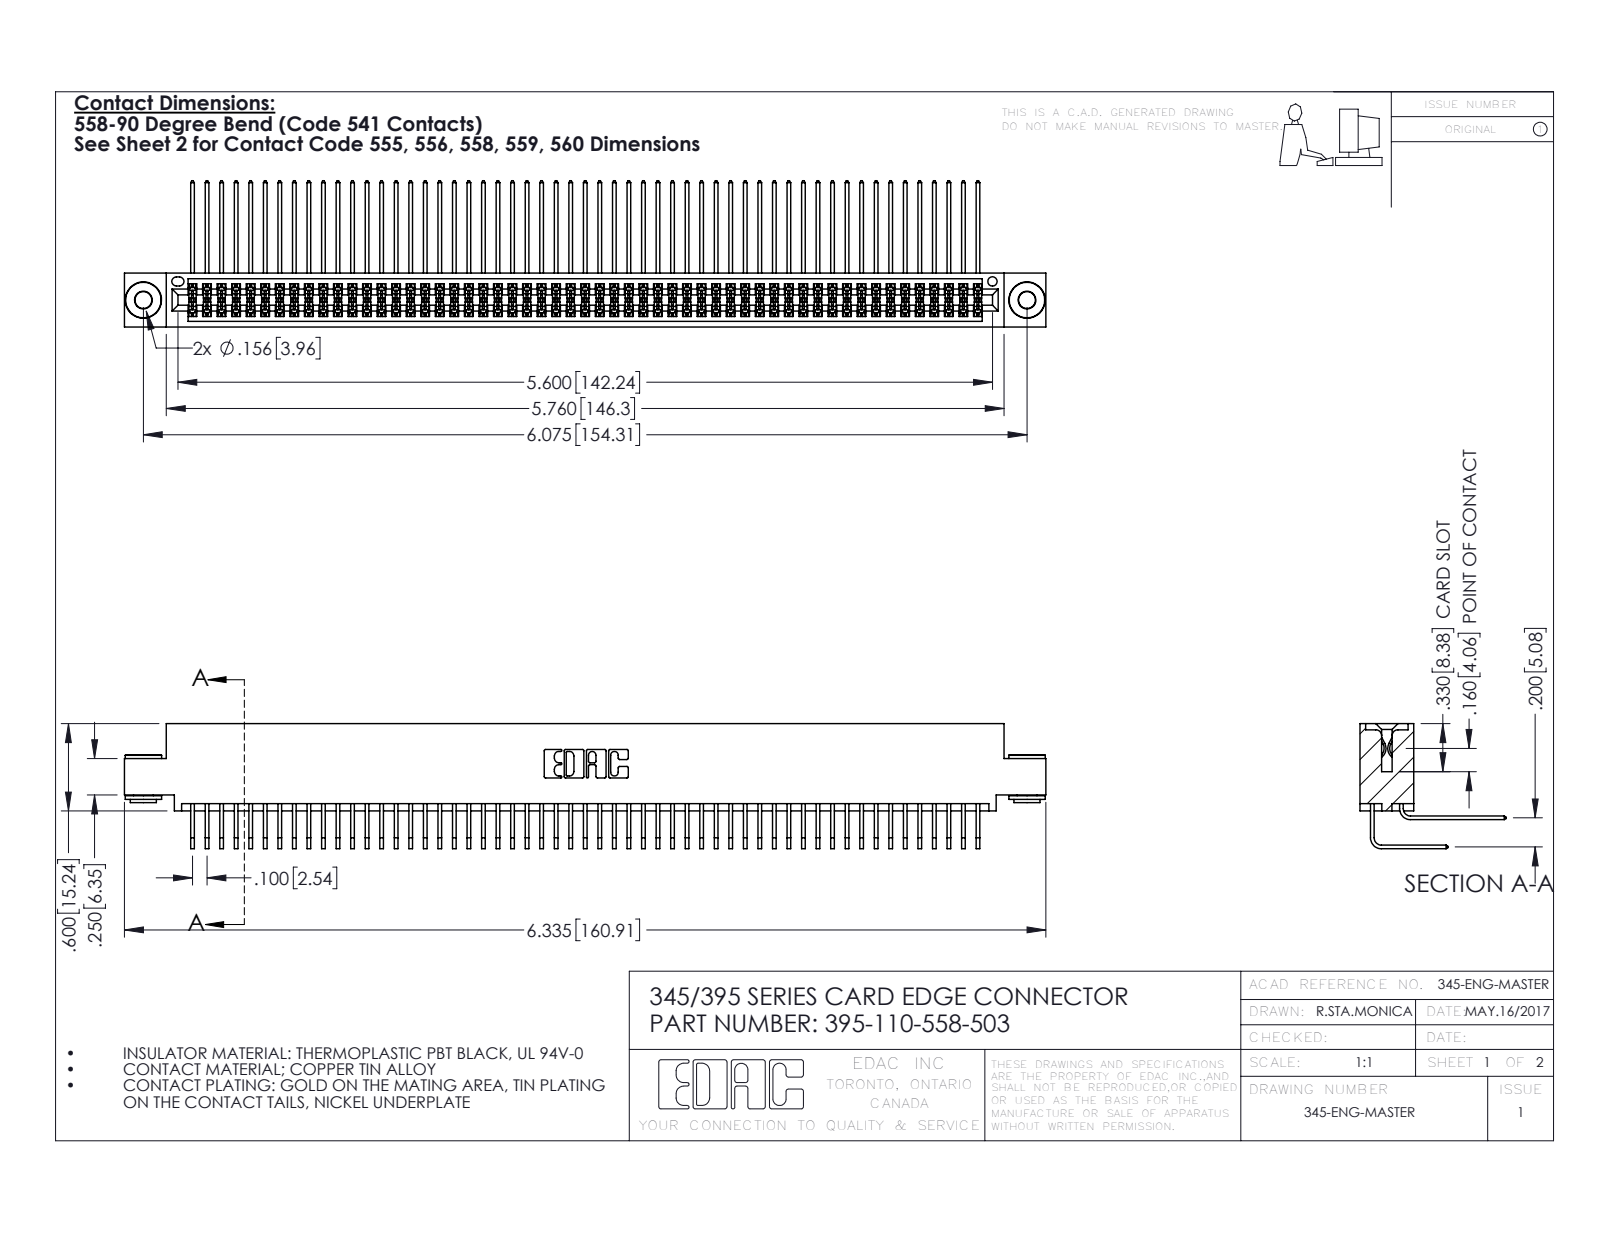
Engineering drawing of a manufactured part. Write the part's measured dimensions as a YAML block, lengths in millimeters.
part_name: "345-292-001_558 559 Tail - 1; 345 Part_0.110 Offset - 0.156 Dia-TH; 345-292-001_558 Tail - 2; 395-110-558-503 (+1 more)"
step_written_by: "SolidWorks 2016 (CONFIG_CONTROL_DESIGN)"
units: millimeters
bodies: {solids: 113, faces: 5888, planar: 3944, cylindrical: 1936, other: 8}
overall_size: [160.9, 25.5, 21.8]
volume: 16300
surface_area: 27680
round_holes:
  - {diameter: 2.9, count: 2}
  - {diameter: 4, count: 2}
  - {diameter: 1.6, count: 1}
round_bosses_or_shafts:
  - {diameter: 6.4, count: 2}
  - {diameter: 4.6, count: 2}
  - {diameter: 3.5, count: 2}
partial_cylinders:
  - {radius: 0.2, count: 165}
  - {radius: 0.3, count: 22}
  - {radius: 0.2, count: 6}
  - {radius: 0.8, count: 6}
  - {radius: 0.7, count: 3}
  - {radius: 0.4, count: 2}
  - {radius: 0.5, count: 2}
  - {radius: 0.6, count: 2}
face_to_face_distances: [1.8, 7.6, 5.1, 0.6, 9.4, 2.5, 6.9, 5.7, 0.6, 4.4]
hole_center_spacings: [6.9, 148.3, 154.3]
